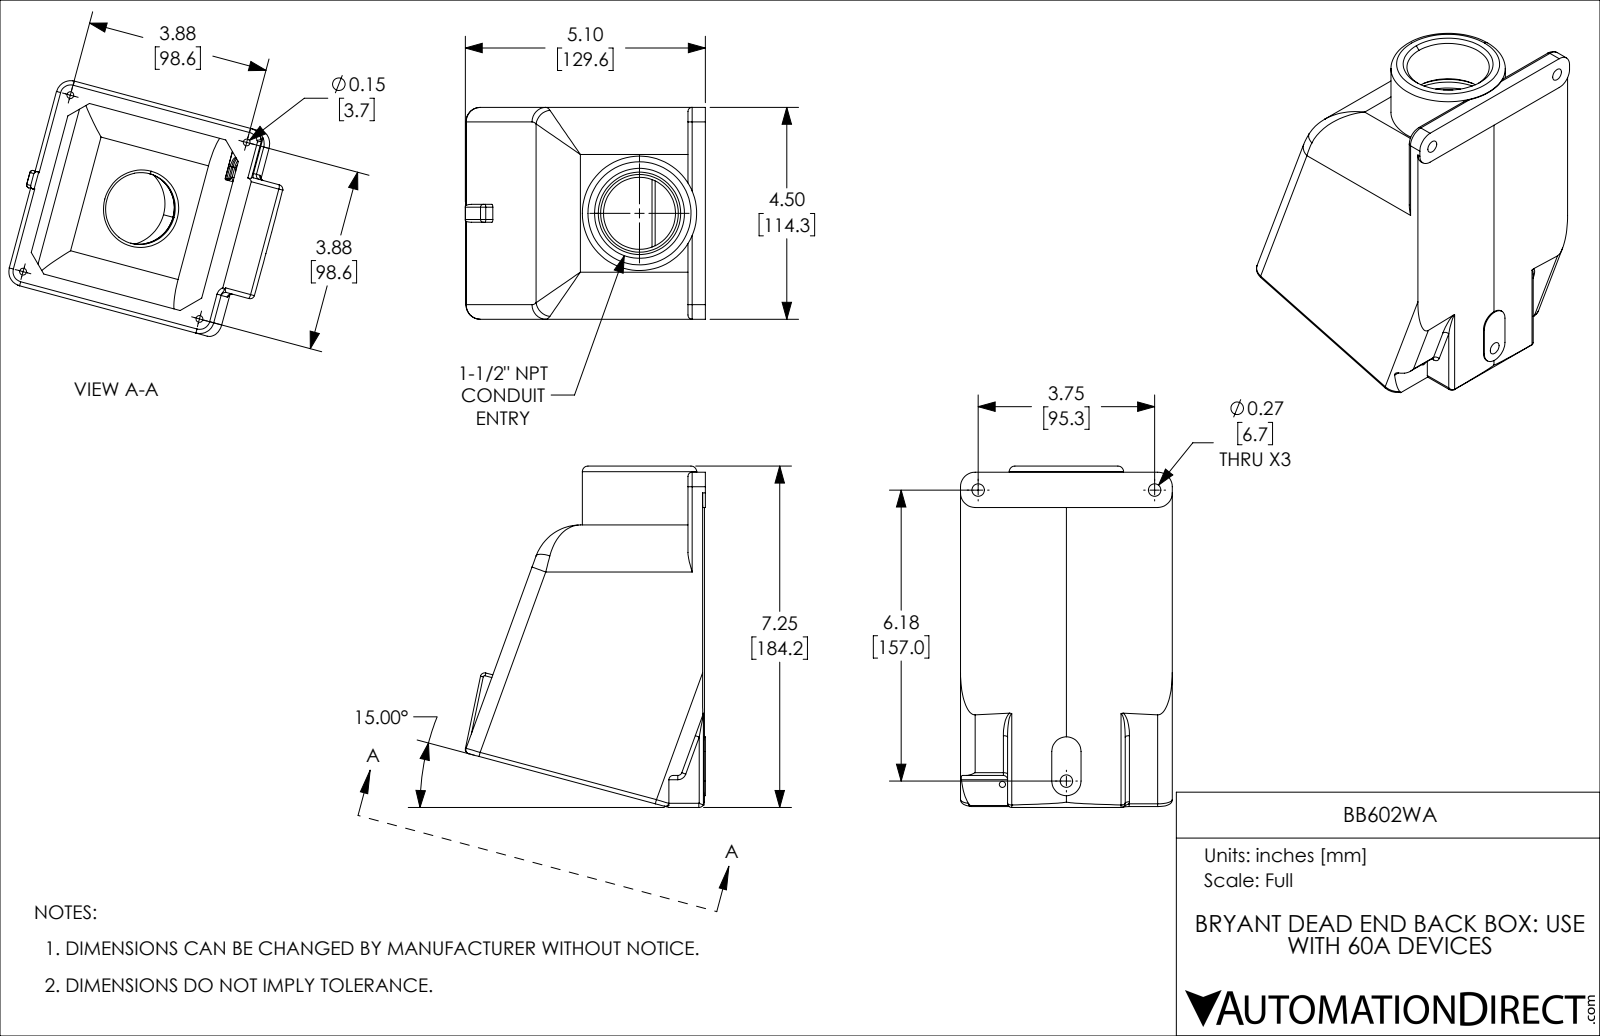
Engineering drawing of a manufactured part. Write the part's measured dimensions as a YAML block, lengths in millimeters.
part_name: "BB602WA"
step_written_by: "SolidWorks 2021 (CONFIG_CONTROL_DESIGN)"
units: millimeters
bodies: {solids: 1, faces: 372, planar: 147, cylindrical: 178, other: 47}
overall_size: [184.2, 129.6, 114.3]
volume: 391800
surface_area: 154100
round_holes:
  - {diameter: 3.7, count: 4}
  - {diameter: 6.7, count: 2}
  - {diameter: 14.2, count: 2}
  - {diameter: 3.3, count: 1}
  - {diameter: 6.7, count: 1}
  - {diameter: 38.9, count: 1}
  - {diameter: 44.5, count: 1}
  - {diameter: 49.8, count: 1}
round_bosses_or_shafts:
  - {diameter: 61.7, count: 1}
partial_cylinders:
  - {radius: 2.3, count: 40}
  - {radius: 7.9, count: 10}
  - {radius: 0.8, count: 6}
  - {radius: 1.5, count: 4}
  - {radius: 6.4, count: 4}
  - {radius: 20.6, count: 3}
  - {radius: 25.4, count: 3}
  - {radius: 2.9, count: 1}
face_to_face_distances: [4.8, 109.5, 104.6, 114.3, 109.1, 5.3, 113.5, 108.7, 4.1, 0.8]
hole_center_spacings: [98.6, 98.6, 139.4, 164, 25.4, 34.6, 95.3, 159.3]
